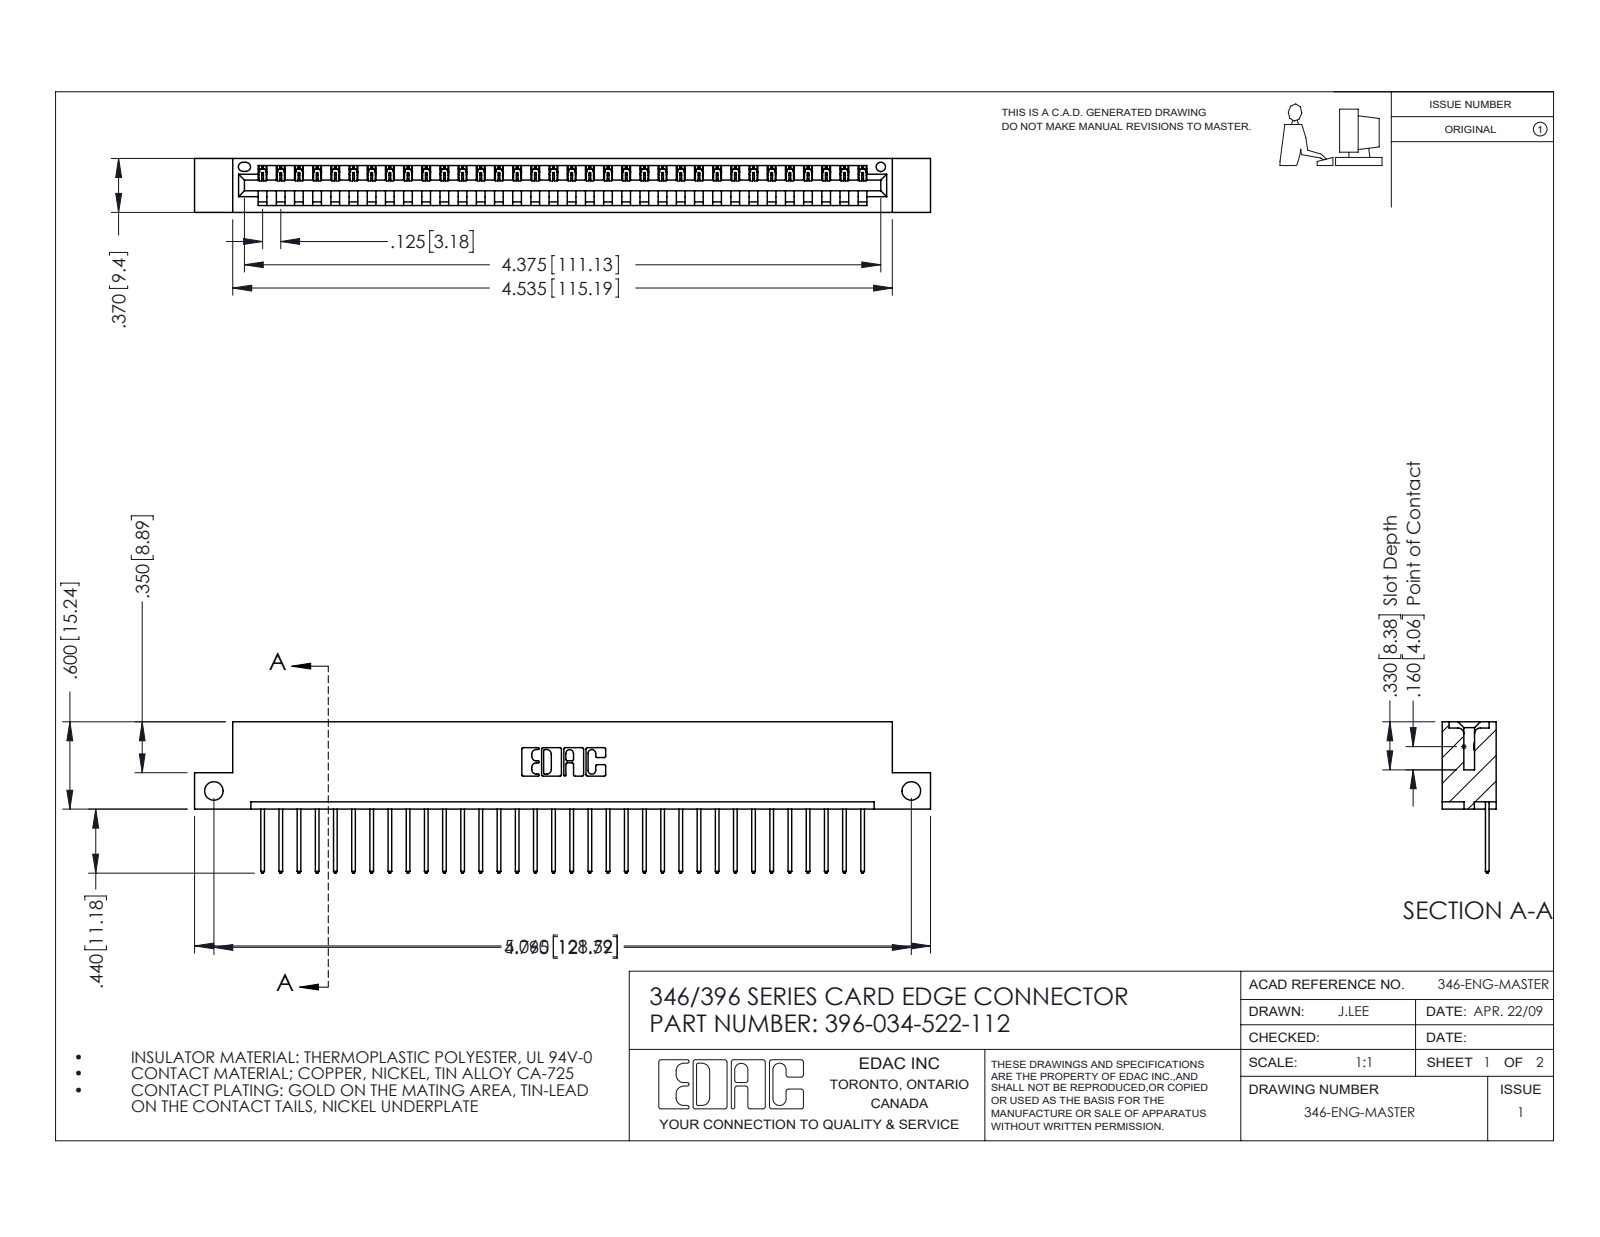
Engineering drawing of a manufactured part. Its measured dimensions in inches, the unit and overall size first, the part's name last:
Units: inches
Overall size (bounding box): 5.06 × 1.04 × 0.37
Round holes (diameter × count): ⌀0.128 ×2, ⌀0.064 ×1
Partial cylindrical surfaces — rounded edges, fillets, slot ends (radius × count): R0.006 ×68, R0.01 ×68, R0.01 ×22, R0.007 ×6, R0.031 ×6, R0.026 ×3, R0.031 ×2, R0.04 ×2
Main face-to-face distances: 0.048, 0.322, 0.37, 0.25, 0.072, 0.298, 0.025, 0.148, 0.222, 0.1
Hole centre spacings: 4.795
Volume: 0.742 in³ · Surface area: 23.4 in²
Bodies: 35 solids, 2094 faces (1436 planar, 658 cylindrical, 0 other)
Part name (STEP PRODUCT): 396-034-522-112; 345-292-001_345-293-122; 346 Part_Flush Mounting Lugs - Side Mount
STEP written by: SolidWorks 2016 (CONFIG_CONTROL_DESIGN)
